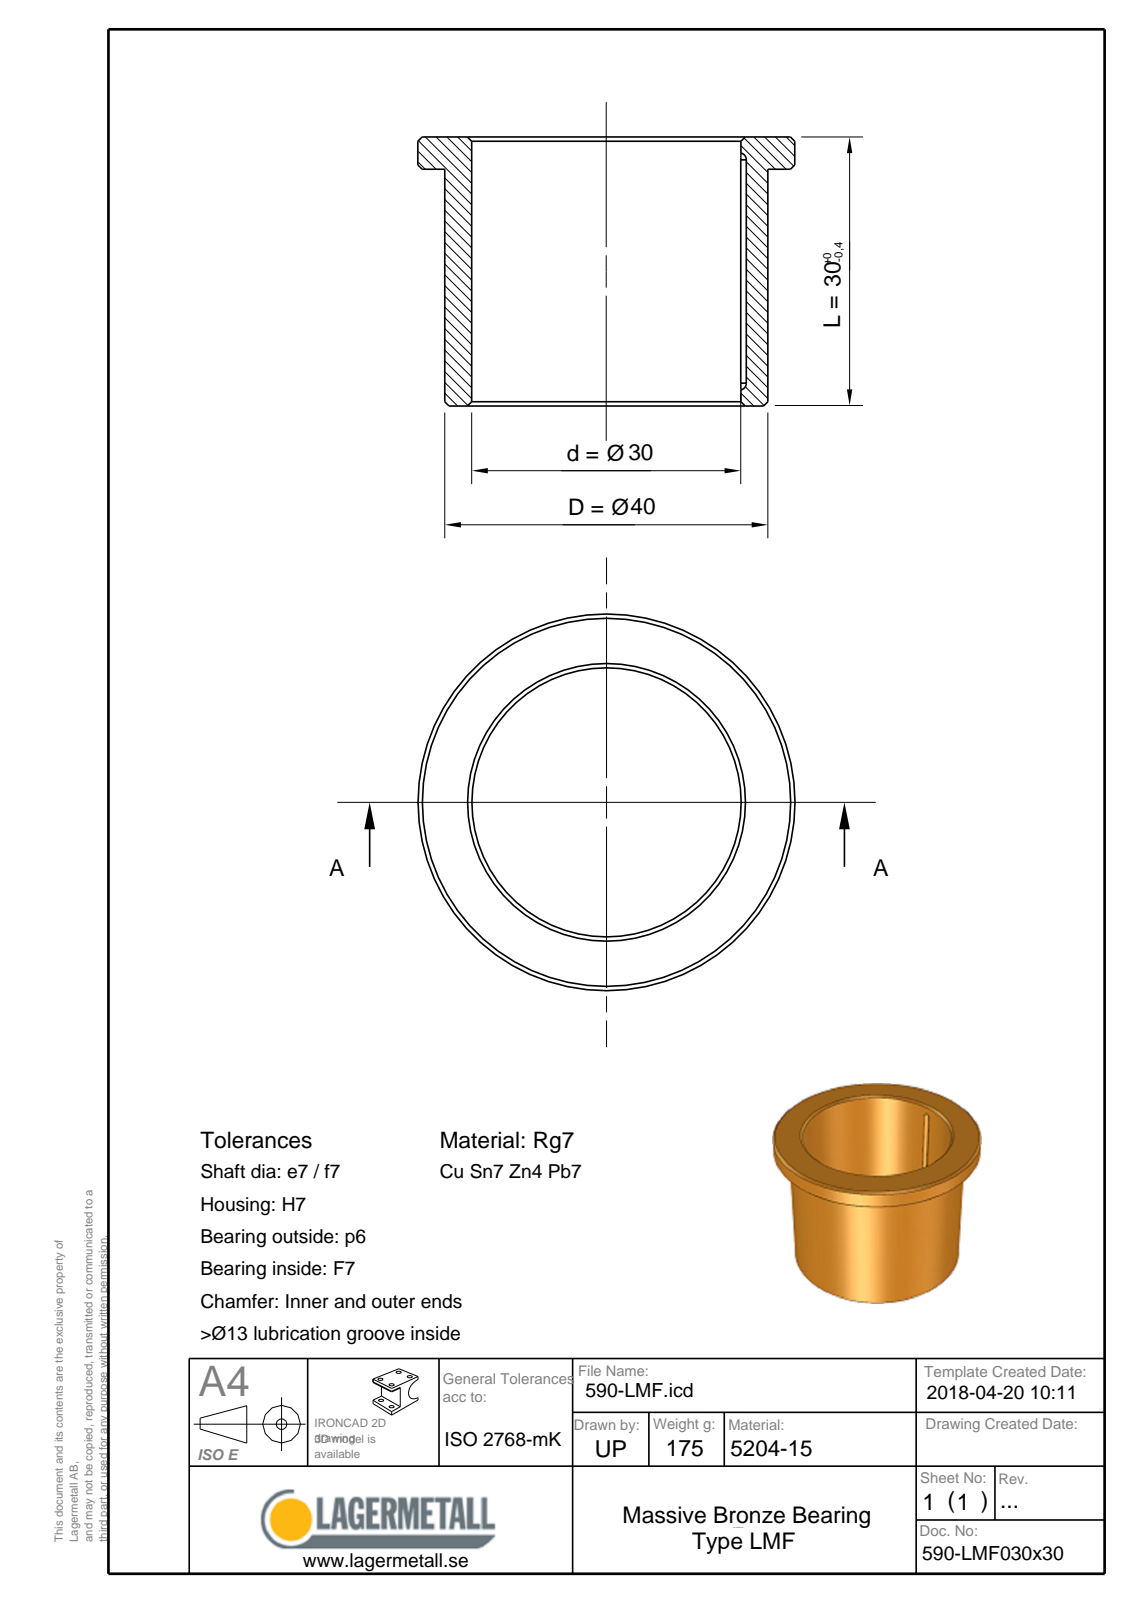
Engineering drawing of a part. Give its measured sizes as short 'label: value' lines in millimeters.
name: 590-LMF030x30
written by: Spatial InterOp 3D (CONFIG_CONTROL_DESIGN)
unit: mm
bodies: 1 solid, 16 faces (4 planar, 5 cylindrical, 7 other)
size: 50 × 50 × 30
volume: 19 905 mm³; area: 9 110 mm²
holes: 1× ⌀30
bosses: 1× ⌀50, 1× ⌀40
rounds: 2× R1.25
face distances: 5, 25, 30
